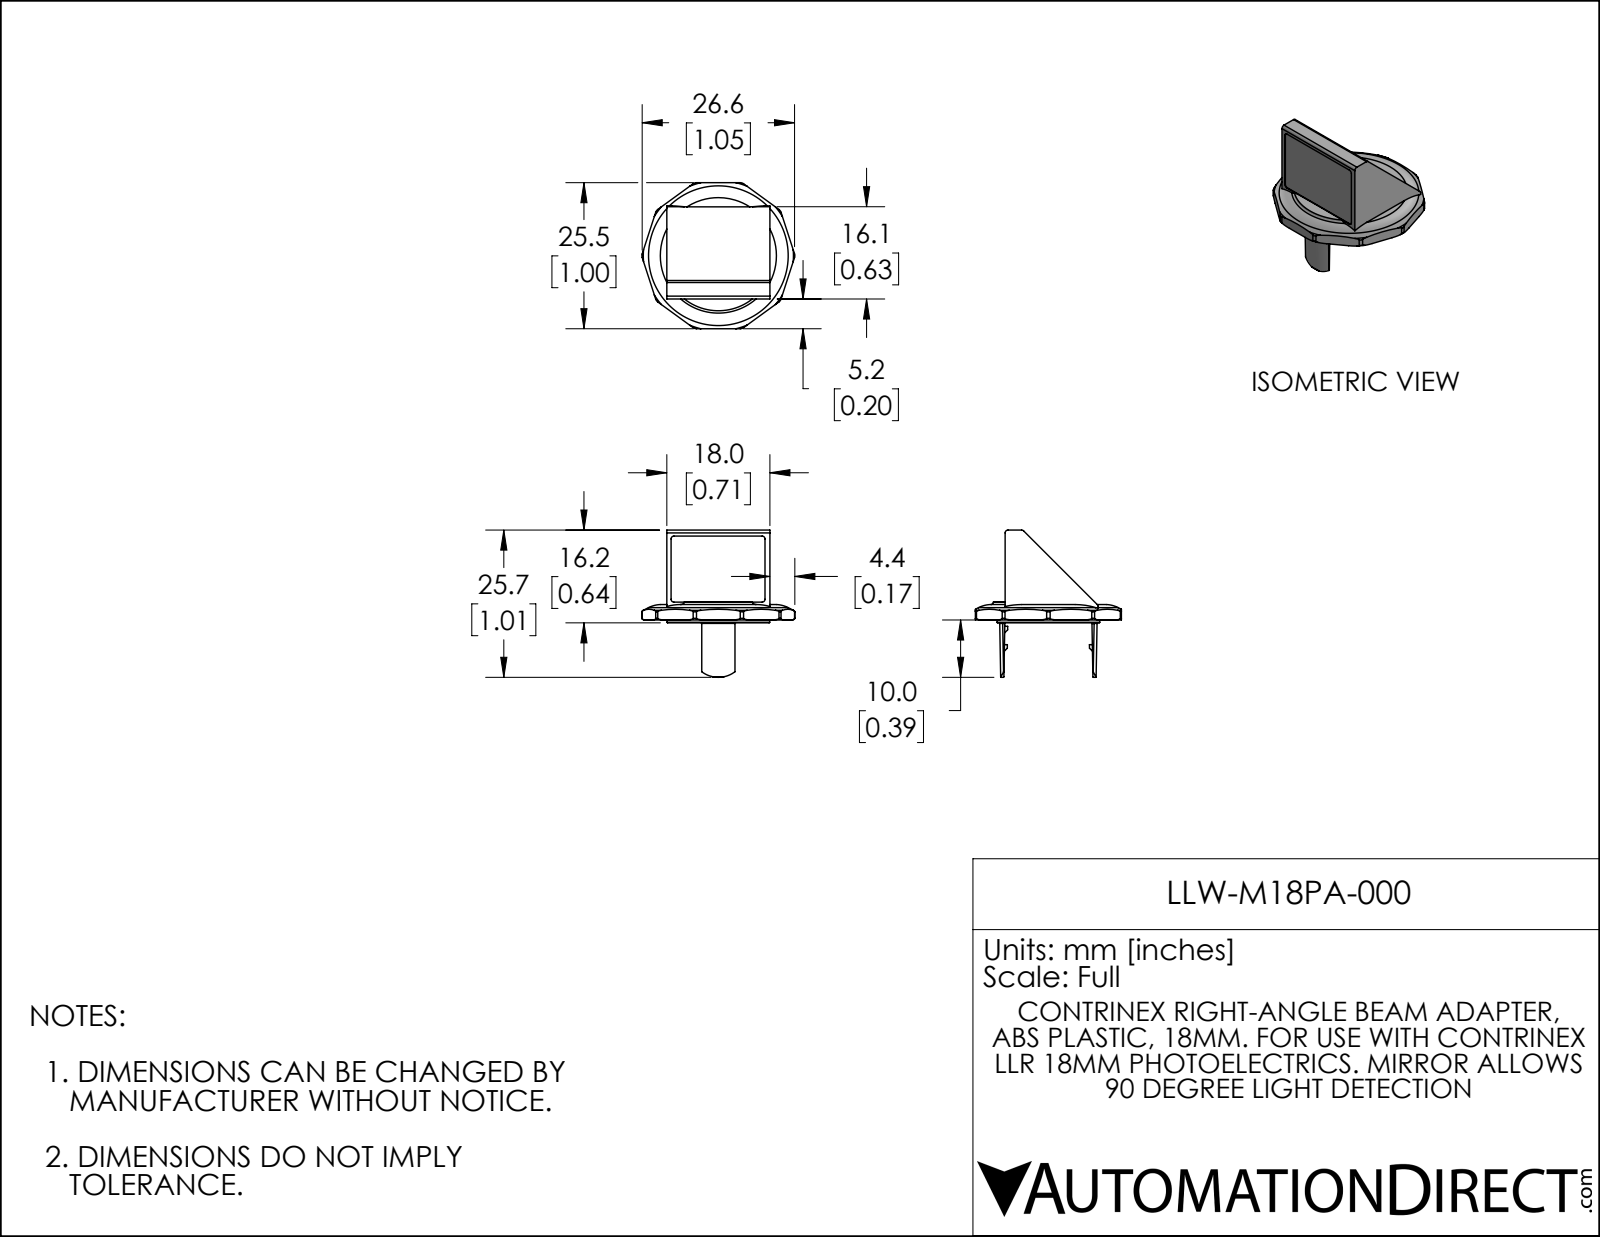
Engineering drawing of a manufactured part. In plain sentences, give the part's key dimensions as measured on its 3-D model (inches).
The part is named "LLW-M18PA-000". Its 3-D file was written by "SolidWorks 2021 (AUTOMOTIVE_DESIGN)". It is 1 solid with 166 faces: 92 planar, 32 cylindrical and 42 other. Overall it measures 1.051 by 1.012 by 1.004 inches. Its volume is 0.093 cubic inches and its surface area 4.411 square inches. Round bosses or shafts: 1 of diameter 0.984, 1 of diameter 0.705. Partial cylindrical surfaces (rounded edges, fillets, slot ends): 10 of radius 0.039, 7 of radius 0.02, 2 of radius 0.004, 2 of radius 0.004, 1 of radius 0.189, 1 of radius 0.307, 1 of radius 0.329. The main face-to-face distances are 0.022, 0.04, 0.043, 0.666, 0.709, 0.623, 0.106, 1.004, 0.618, 0.512.
